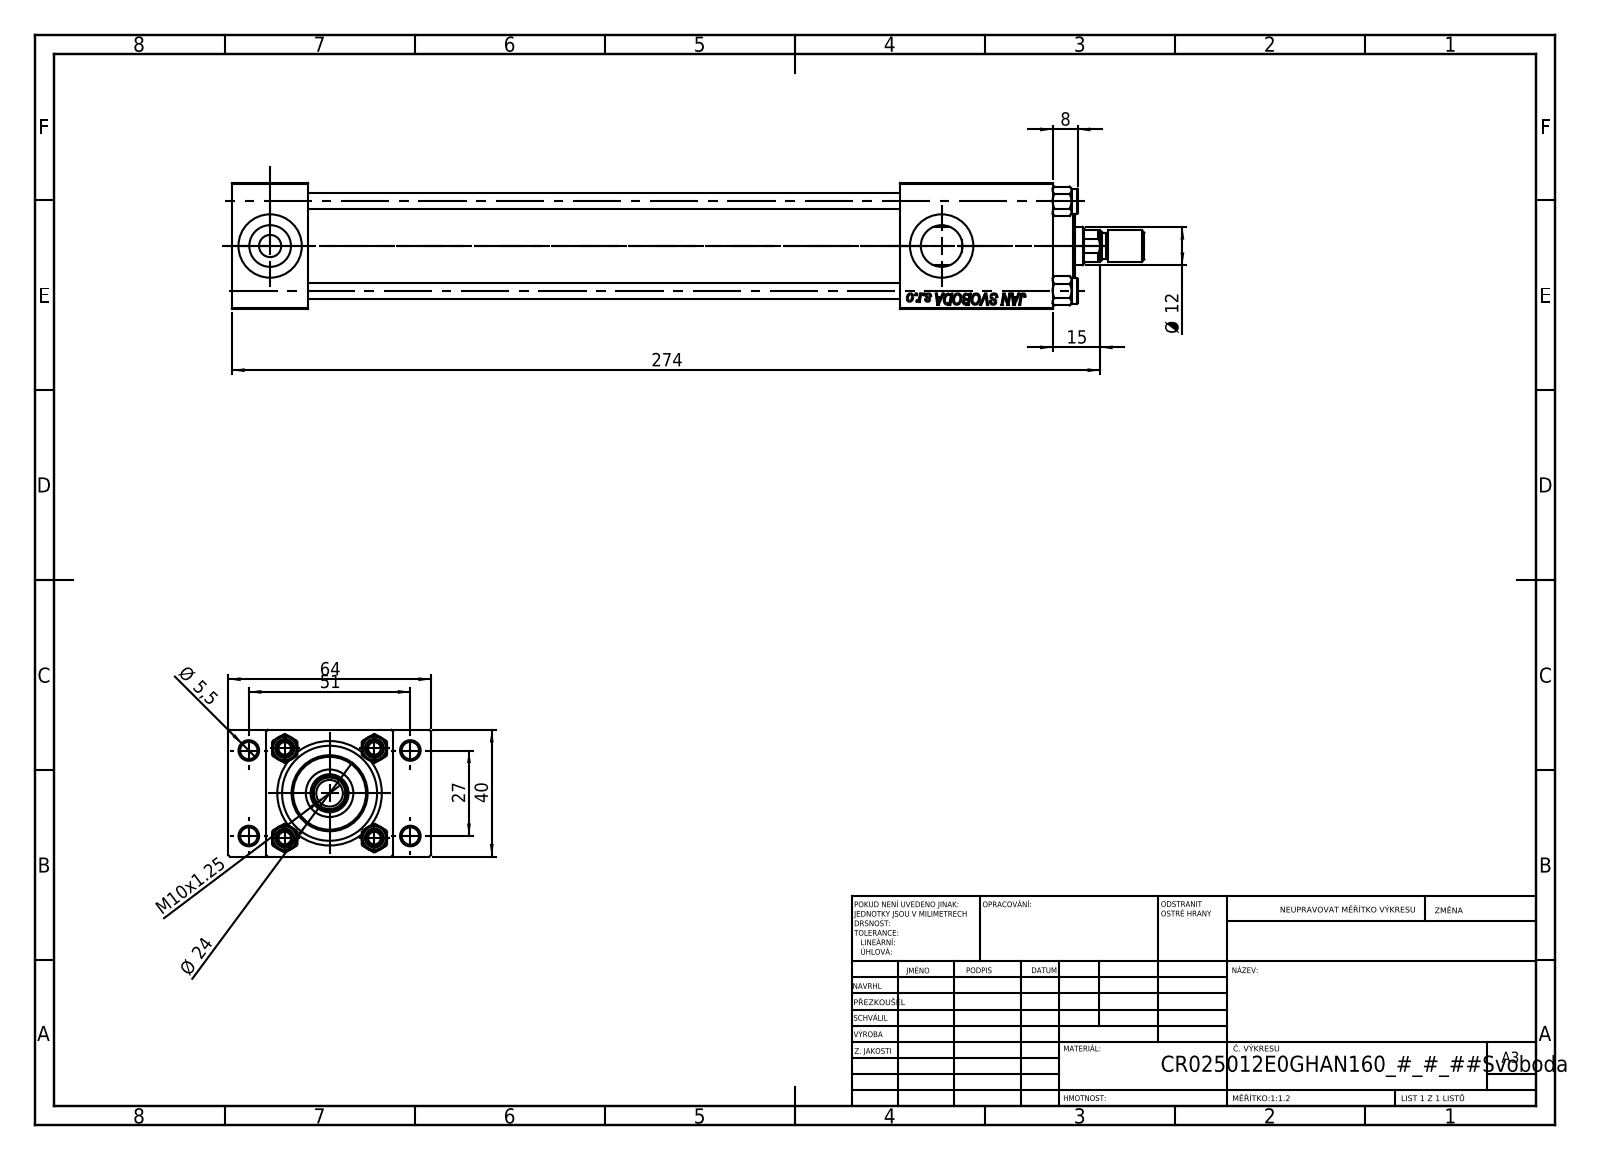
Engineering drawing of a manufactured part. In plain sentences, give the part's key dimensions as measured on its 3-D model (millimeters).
The part is named "V215_VC_A; V215CR_VCP_E; ROD_END_AH; NUT_M5_E (+2 more)". Its 3-D file was written by "SolidWorks 2019 (CONFIG_CONTROL_DESIGN)". It is 12 solids with 1149 faces: 501 planar, 90 cylindrical and 558 other. Overall it measures 288 by 64 by 40 millimeters. Its volume is 228 339 cubic millimeters and its surface area 101 683 square millimeters. Round holes: 4 of diameter 5, 4 of diameter 5.5, 3 of diameter 20, 2 of diameter 7, 2 of diameter 13.16, 1 of diameter 6.5, 1 of diameter 12, 1 of diameter 15, 1 of diameter 25, 1 of diameter 30. Round bosses or shafts: 5 of diameter 8, 1 of diameter 31, 1 of diameter 24, 1 of diameter 10. Partial cylindrical surfaces (rounded edges, fillets, slot ends): 1 of radius 5.5. The main face-to-face distances are 40, 24, 12, 52, 259, 235, 230.3, 206.3, 28.7, 211. The hole center spacings are 11.37, 20.01, 28.3, 28.85, 29.89, 39.66, 48.34, 27.
